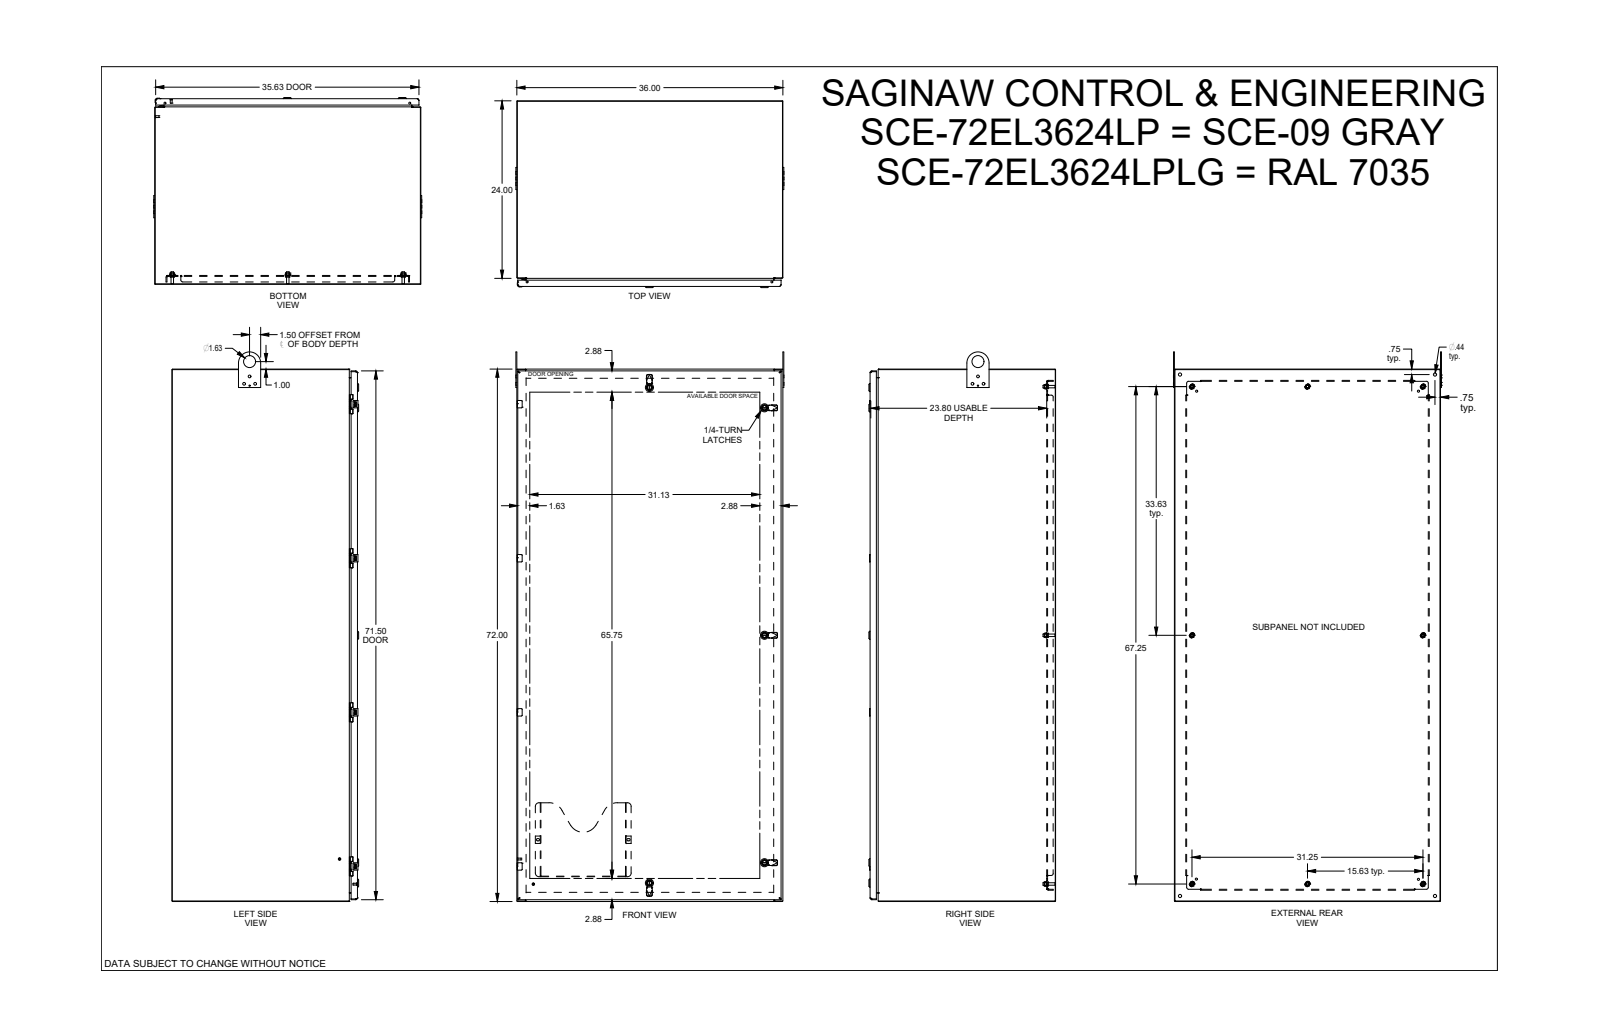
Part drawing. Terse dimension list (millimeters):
name: SCE-72EL3624LP
written by: SolidWorks 2019 (CONFIG_CONTROL_DESIGN)
unit: mm
bodies: 0 solids, 5593 faces (2661 planar, 1568 cylindrical, 1364 other)
size: 1887.5 × 921.1 × 641.5
holes: 8× ⌀4.4, 8× ⌀5.2, 8× ⌀6.2, 8× ⌀6.8, 8× ⌀9.3, 8× ⌀9.5, 8× ⌀12.7, 5× ⌀5, 5× ⌀8, 5× ⌀10, 5× ⌀16.1, 4× ⌀1
bosses: 12× ⌀4.3, 8× ⌀9.3, 8× ⌀8.4, 8× ⌀6.4, 8× ⌀6.1, 5× ⌀28, 5× ⌀22, 5× ⌀20.4
rounds: 136× R0.3, 70× R0.3, 52× R0.5, 42× R0.4, 27× R0.8, 20× R0.6, 20× R2.5, 20× R4
face distances: 1.9, 1.9, 912.5, 2.6, 633, 634.9, 637.5, 635.6, 3.2, 28.6
hole spacings: 529.2, 1058.3, 529.2, 1587.5, 1.3, 12.5, 12.5, 25
